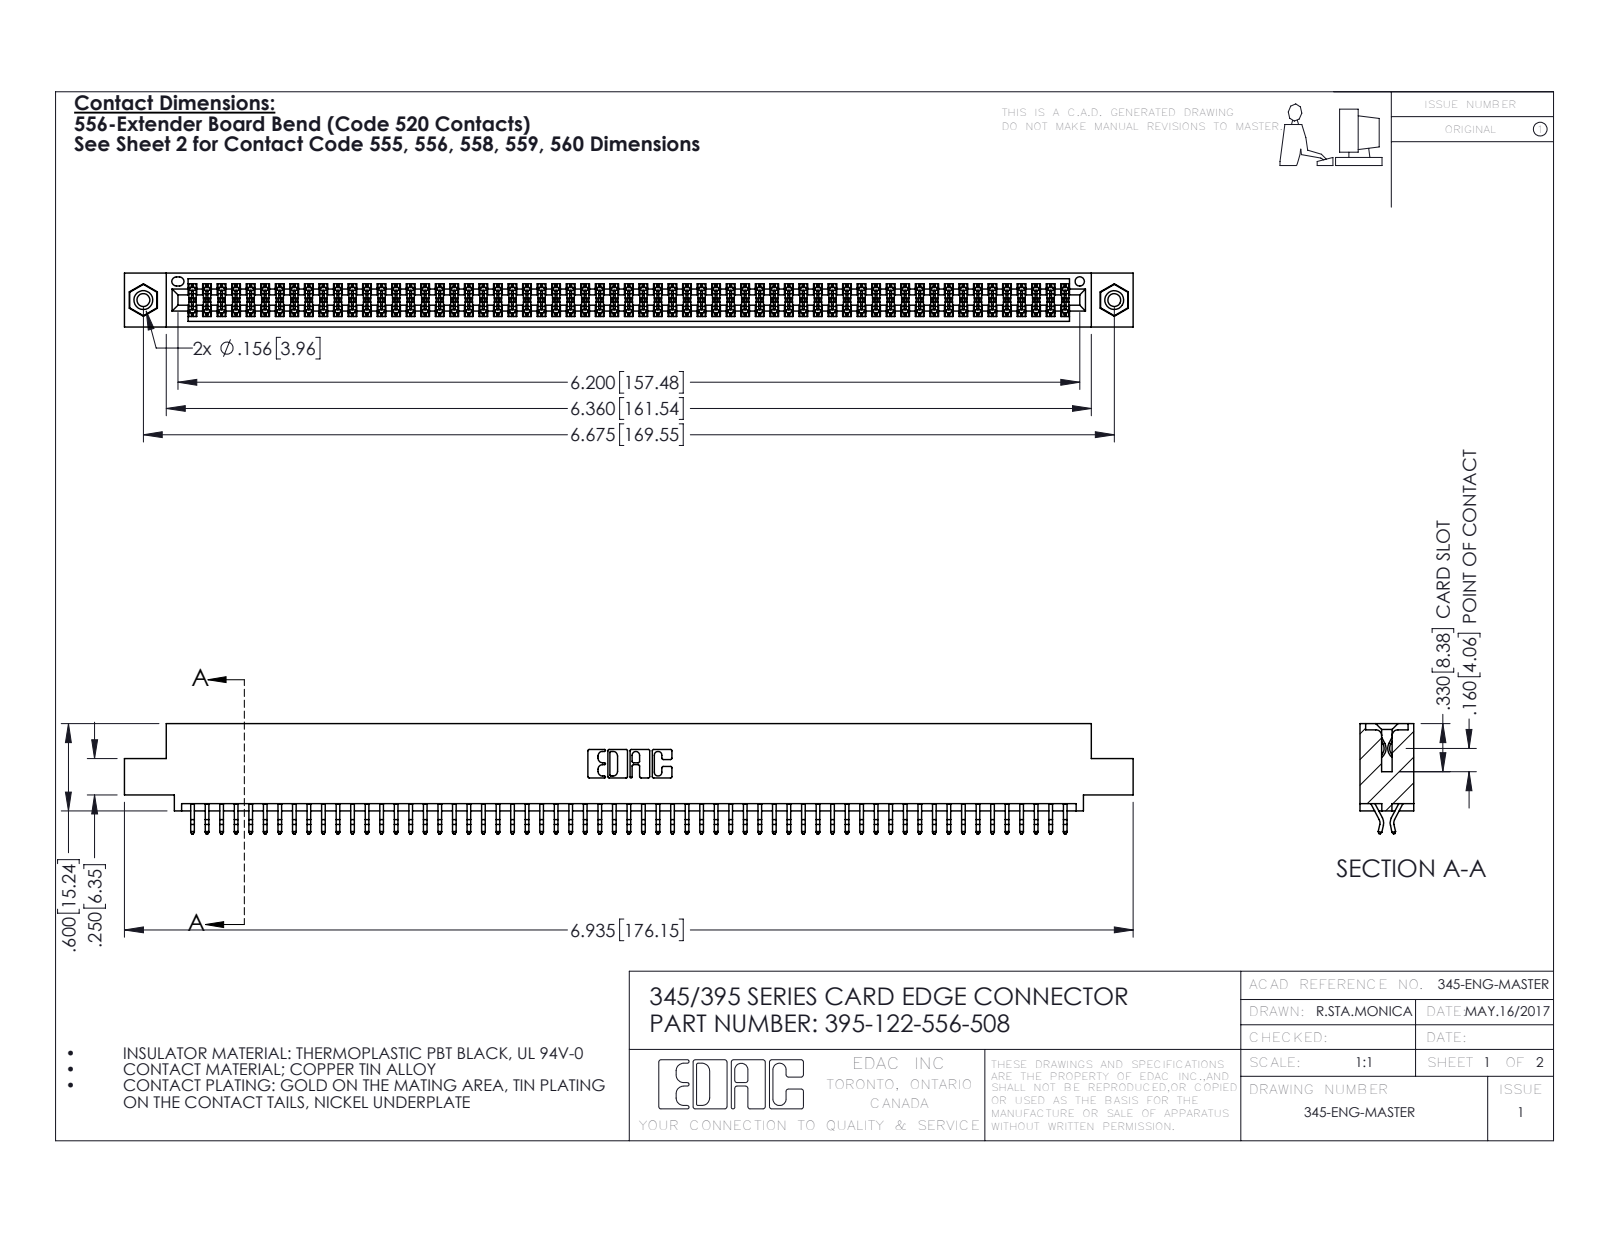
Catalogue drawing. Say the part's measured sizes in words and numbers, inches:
The part is named "345-292-001_556 Tail; 345-250-001_345-250-003-102; 345 Part_0.110 Offset - 0.156 Dia-TI; 395-122-556-508". Its 3-D file was written by "SolidWorks 2016 (CONFIG_CONTROL_DESIGN)". It is 125 solids with 7022 faces: 4630 planar, 2376 cylindrical and 16 other. Overall it measures 6.935 by 0.757 by 0.37 inches. Its volume is 1.05 cubic inches and its surface area 39.98 square inches. Round holes: 2 of diameter 0.089, 2 of diameter 0.125, 2 of diameter 0.156, 1 of diameter 0.064. Round bosses or shafts: 2 of diameter 0.155. Partial cylindrical surfaces (rounded edges, fillets, slot ends): 183 of radius 0.006, 22 of radius 0.01, 6 of radius 0.007, 6 of radius 0.031, 3 of radius 0.026, 2 of radius 0.01, 2 of radius 0.014, 2 of radius 0.019. The main face-to-face distances are 0.072, 0.298, 0.37, 0.2, 0.025, 0.098, 0.272, 0.225, 0.175, 0.149. The hole center spacings are 0.27, 6.439, 6.675.
